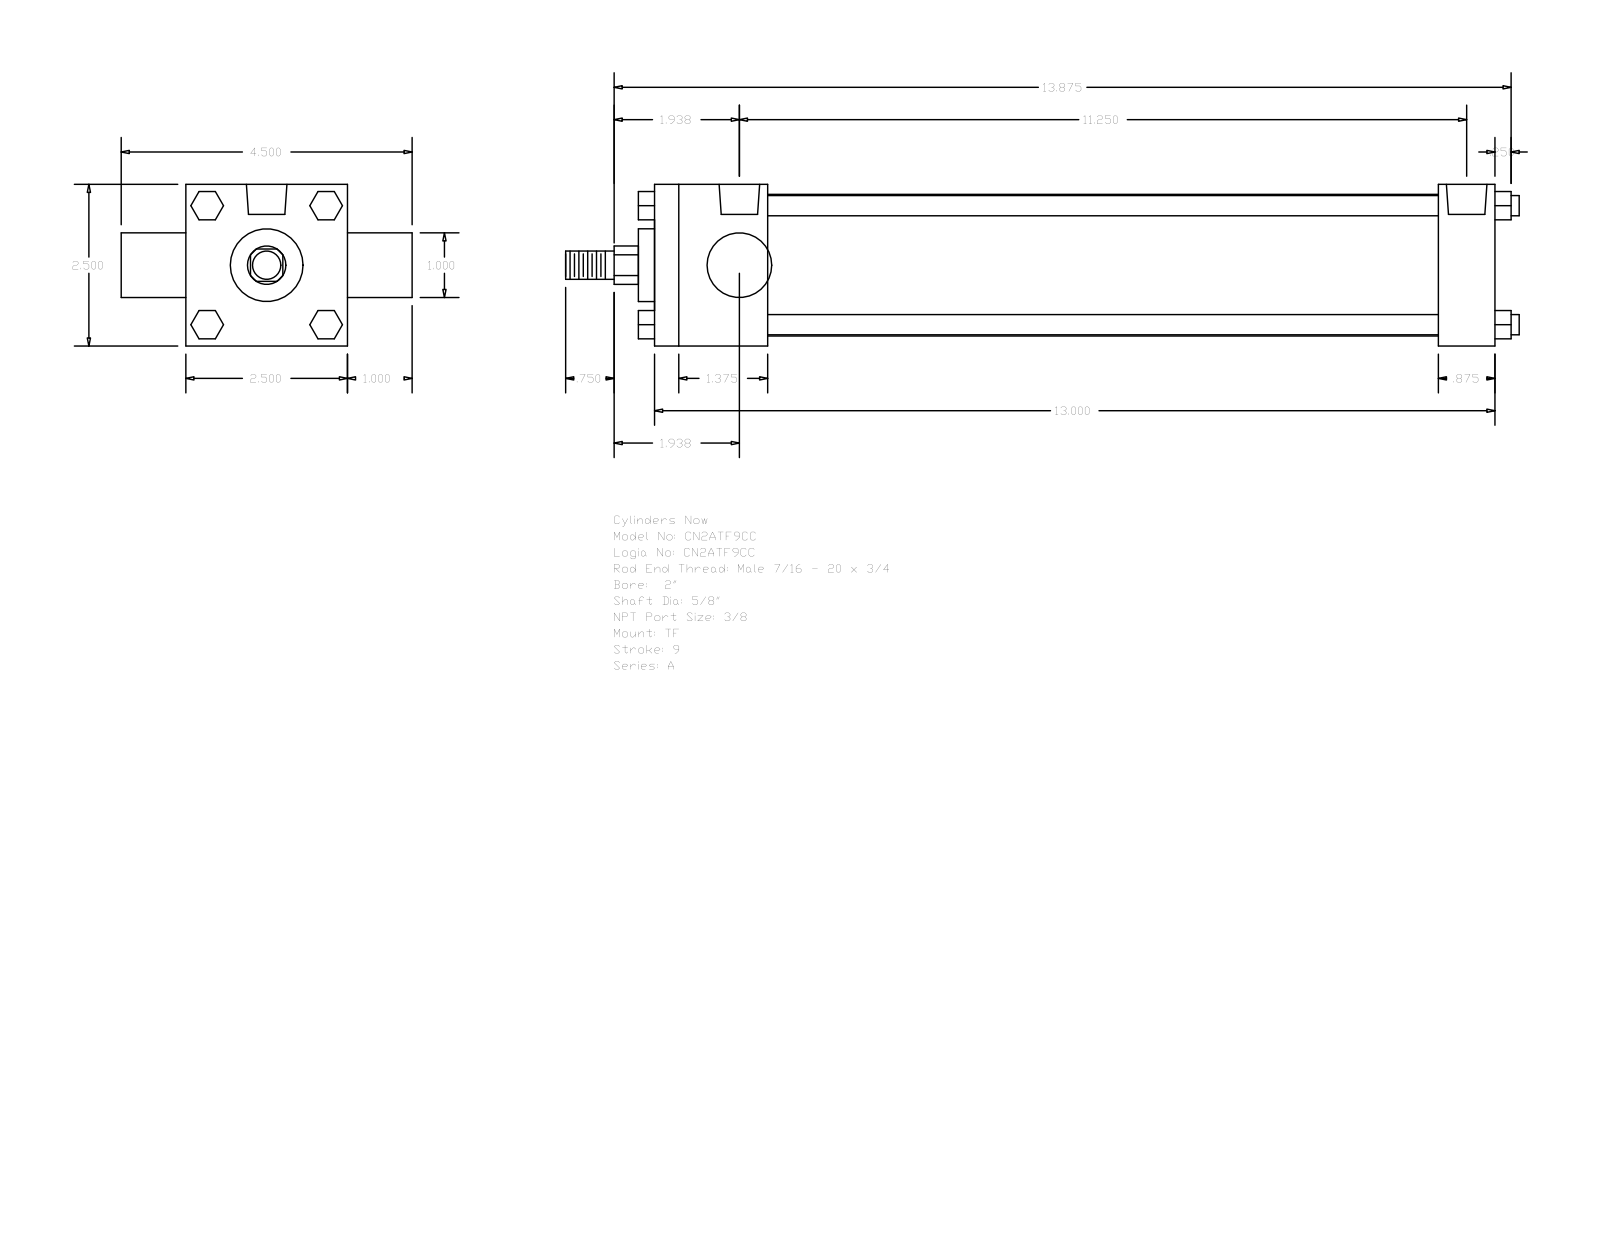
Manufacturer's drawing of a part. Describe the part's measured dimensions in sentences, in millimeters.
The part is named "A_TF__0200_0.625". Its 3-D file was written by "GSSL Pune (CONFIG_CONTROL_DESIGN)". It is 0 solids with 120 faces: 92 planar, 28 cylindrical and 0 other. Overall it measures 374.65 by 114.3 by 63.5 millimeters. Round holes: 3 of diameter 5.56, 2 of diameter 15.93. Round bosses or shafts: 4 of diameter 7.94, 1 of diameter 55.63, 1 of diameter 28.57, 1 of diameter 25.4, 1 of diameter 15.88, 1 of diameter 11.11. Partial cylindrical surfaces (rounded edges, fillets, slot ends): 1 of radius 7.54. The main face-to-face distances are 63.5, 330.19, 44.45, 307.97, 263.52, 285.74, 22.22, 25.4, 88.9, 50.8. The hole center spacings are 3.97, 3.98, 277.8, 281.77, 281.78, 285.75.
